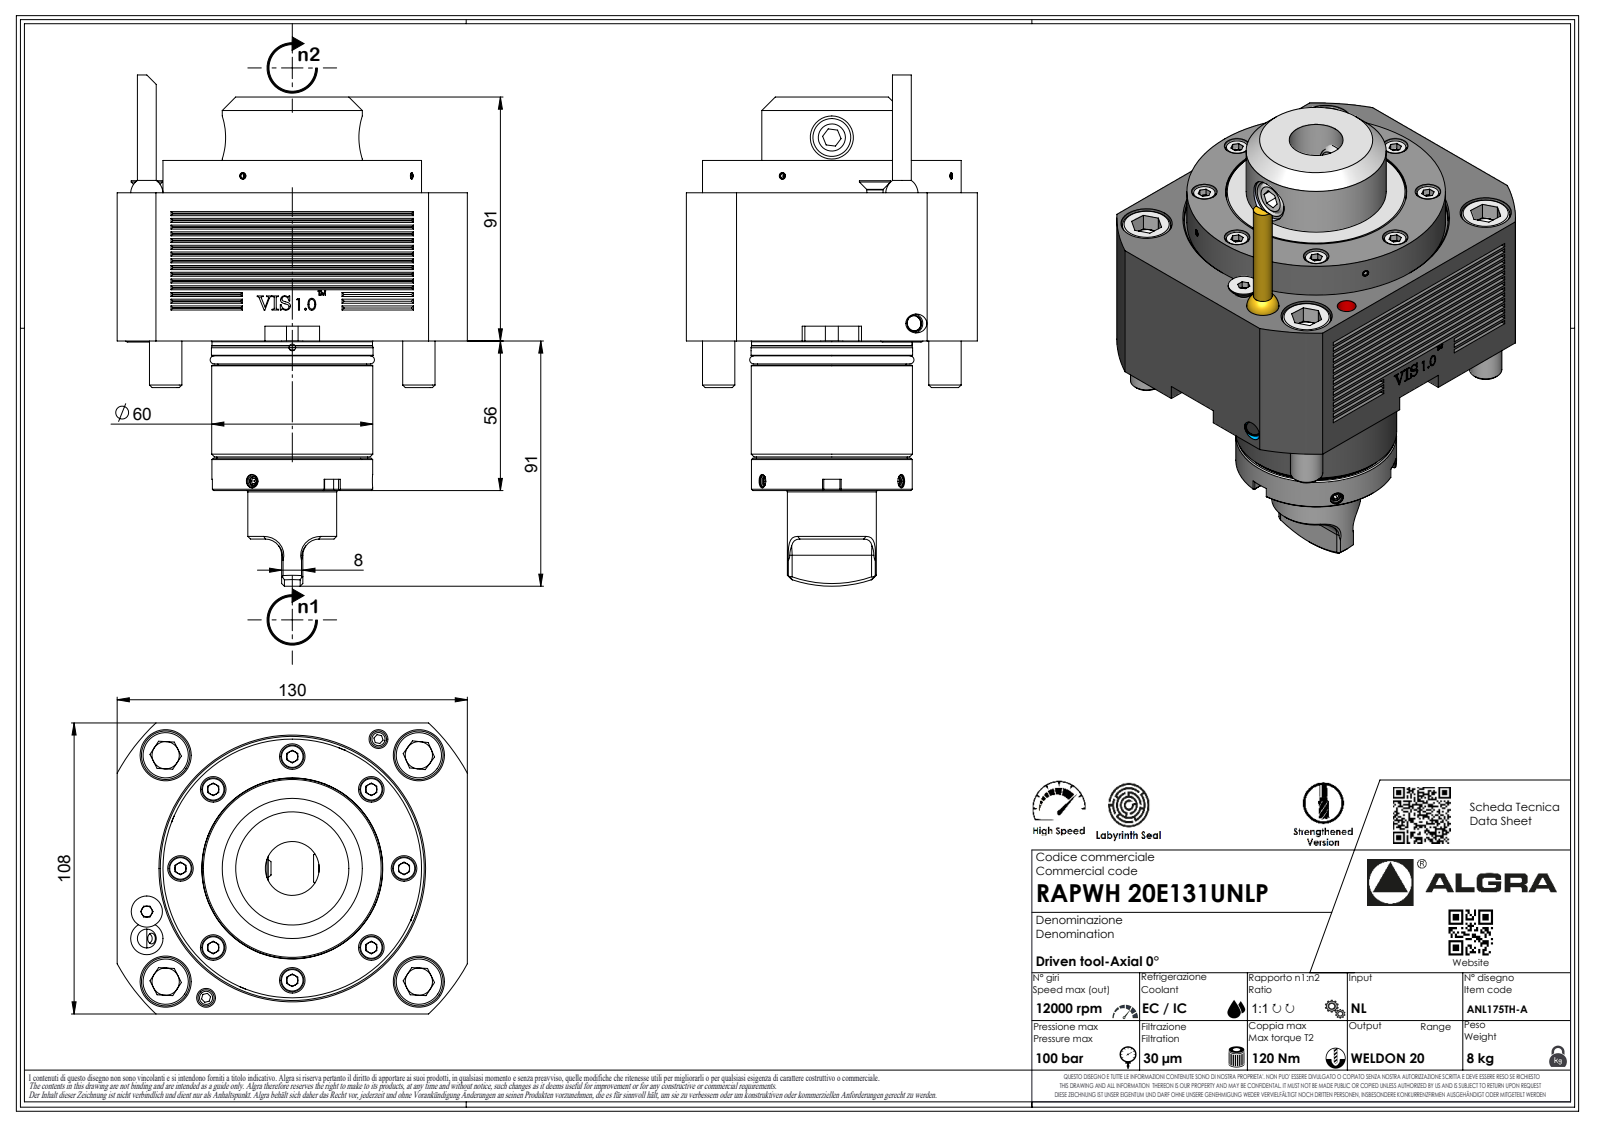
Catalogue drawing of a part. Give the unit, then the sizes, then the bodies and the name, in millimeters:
Units: millimetres
Overall size (bounding box): 189.7 × 130 × 108
Round holes (diameter × count): ⌀2.1 ×1, ⌀4 ×1
Round bosses / shafts (diameter × count): ⌀12 ×4, ⌀96 ×1, ⌀60 ×1, ⌀59.8 ×1, ⌀52 ×1, ⌀33 ×1, ⌀7 ×1, ⌀6.37 ×1
Partial cylindrical surfaces — rounded edges, fillets, slot ends (radius × count): R0.33 ×7, R0.52 ×7, R3.7 ×7, R6 ×6, R0.21 ×1, R2 ×1, R46 ×1, R74 ×1
Main face-to-face distances: 55, 108, 67, 12, 130, 55.5, 110.5, 122.5, 145.5, 90
Volume: 1 065 000 mm³ · Surface area: 75 051 mm²
Bodies: 1 solid, 390 faces (252 planar, 50 cylindrical, 88 other)
Part name (STEP PRODUCT): RAPWH20E131UNLP
STEP written by: SolidWorks 2023 (AUTOMOTIVE_DESIGN)
